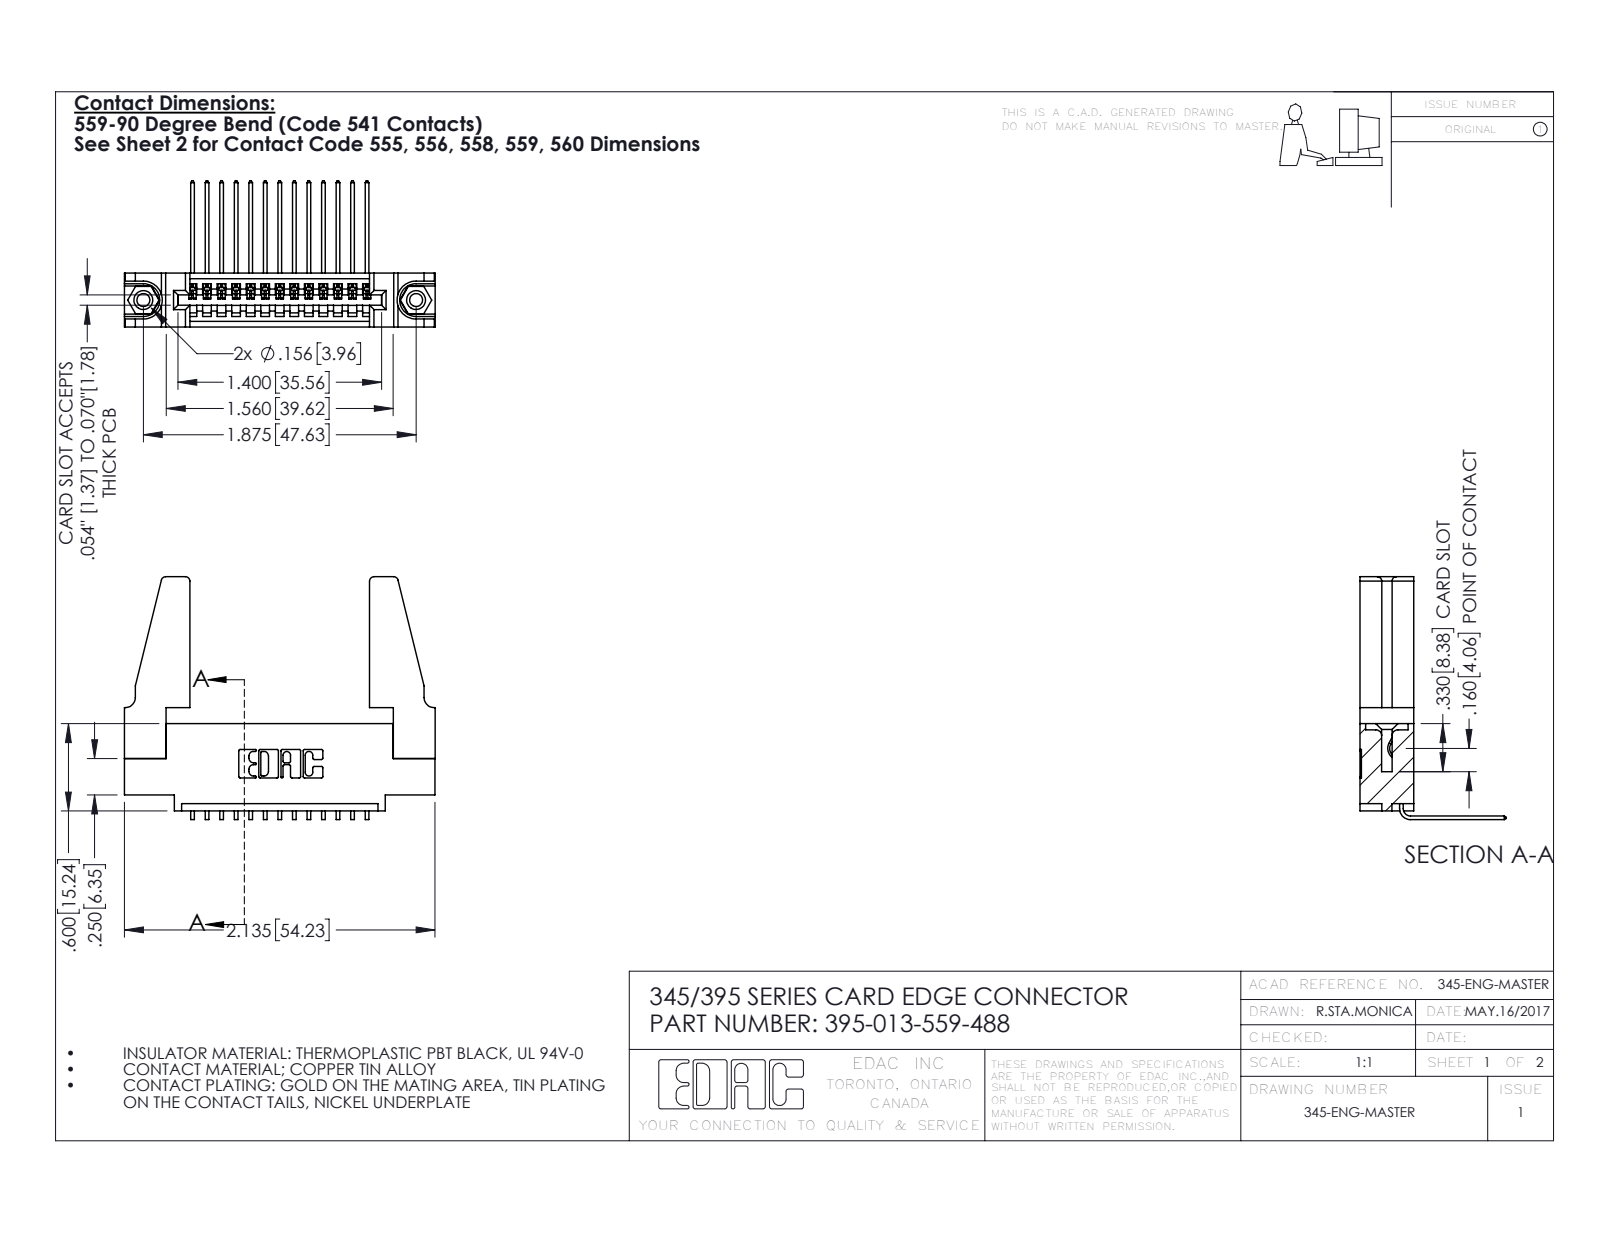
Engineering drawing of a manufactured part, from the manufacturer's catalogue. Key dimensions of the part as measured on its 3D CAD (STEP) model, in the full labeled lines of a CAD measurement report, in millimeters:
Part name (STEP PRODUCT): 345-250-001_345-250-001-102; 345-220-078_345-220-088; 395-013-559-488; 345-292-001_558 559 Tail - 1 (+1 more)
STEP written by: SolidWorks 2016 (CONFIG_CONTROL_DESIGN)
Units: millimetres
Bodies: 18 solids, 1034 faces (702 planar, 316 cylindrical, 16 other)
Overall size (bounding box): 54.3 × 42.4 × 25.5
Volume: 8 140 mm³ · Surface area: 9 561 mm²
Round holes (diameter × count): ⌀2.3 ×2, ⌀3.2 ×2, ⌀4 ×2, ⌀1.6 ×1
Round bosses / shafts (diameter × count): ⌀3.9 ×2
Partial cylindrical surfaces — rounded edges, fillets, slot ends (radius × count): R0.2 ×26, R0.3 ×22, R0.8 ×8, R0.2 ×6, R0.8 ×6, R0.7 ×3, R0.8 ×2, R1 ×2
Main face-to-face distances: 9.4, 1.8, 7.6, 5.1, 2.5, 6.9, 0.6, 5.7, 3.8, 3.8
Hole centre spacings: 6.9, 41.7, 47.6
